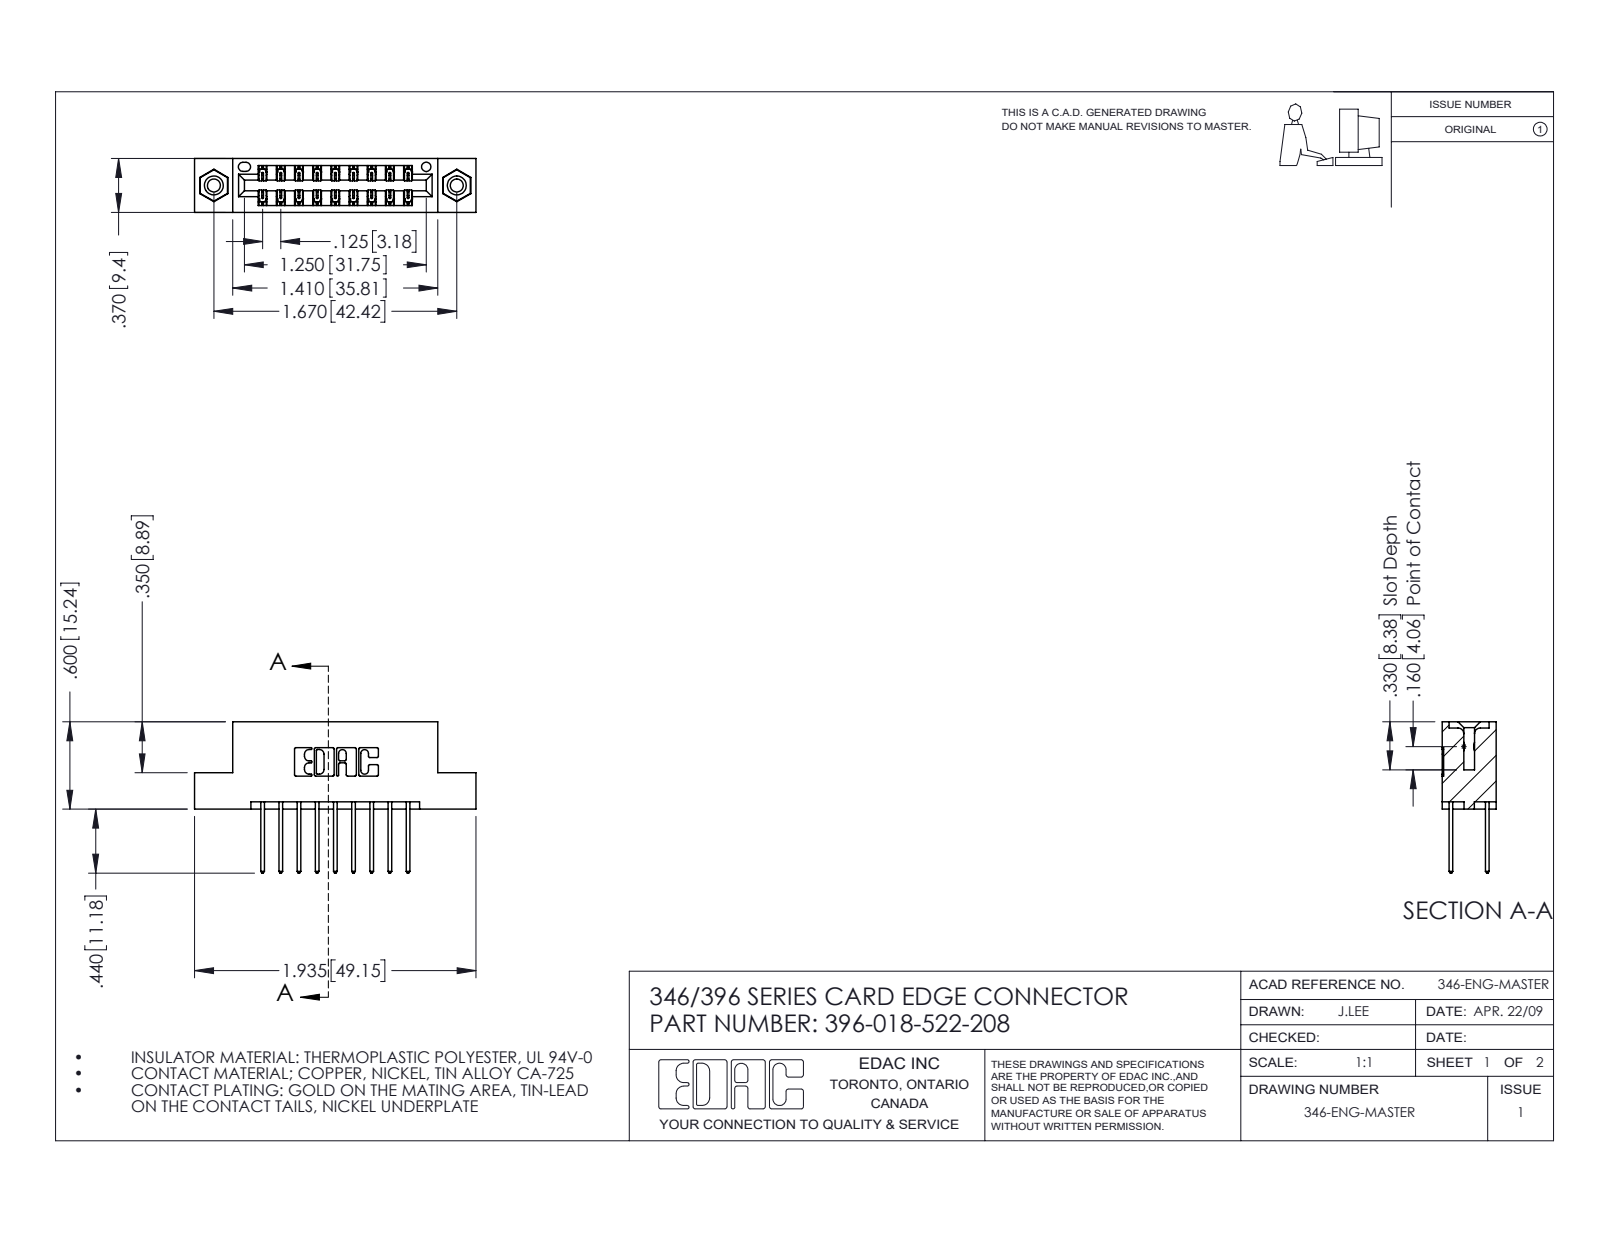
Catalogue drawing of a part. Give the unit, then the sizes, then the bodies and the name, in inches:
Units: inches
Overall size (bounding box): 1.935 × 1.04 × 0.37
Round holes (diameter × count): ⌀0.089 ×2, ⌀0.125 ×2, ⌀0.156 ×2, ⌀0.064 ×1
Round bosses / shafts (diameter × count): ⌀0.155 ×2
Partial cylindrical surfaces — rounded edges, fillets, slot ends (radius × count): R0.006 ×27, R0.01 ×22, R0.01 ×18, R0.007 ×6, R0.031 ×6, R0.026 ×3, R0.014 ×2, R0.022 ×2
Main face-to-face distances: 0.25, 0.048, 0.322, 0.37, 0.072, 0.298, 0.025, 0.275, 0.148, 0.222
Hole centre spacings: 0.246, 1.465, 1.67
Volume: 0.279 in³ · Surface area: 9.308 in²
Bodies: 21 solids, 1118 faces (738 planar, 364 cylindrical, 16 other)
Part name (STEP PRODUCT): 396-018-522-208; 345-250-001_345-250-003-102; 346 Part_Flush Mounting Lugs - 0.156 Dia-TI; 345-292-001_345-293-122
STEP written by: SolidWorks 2016 (CONFIG_CONTROL_DESIGN)
